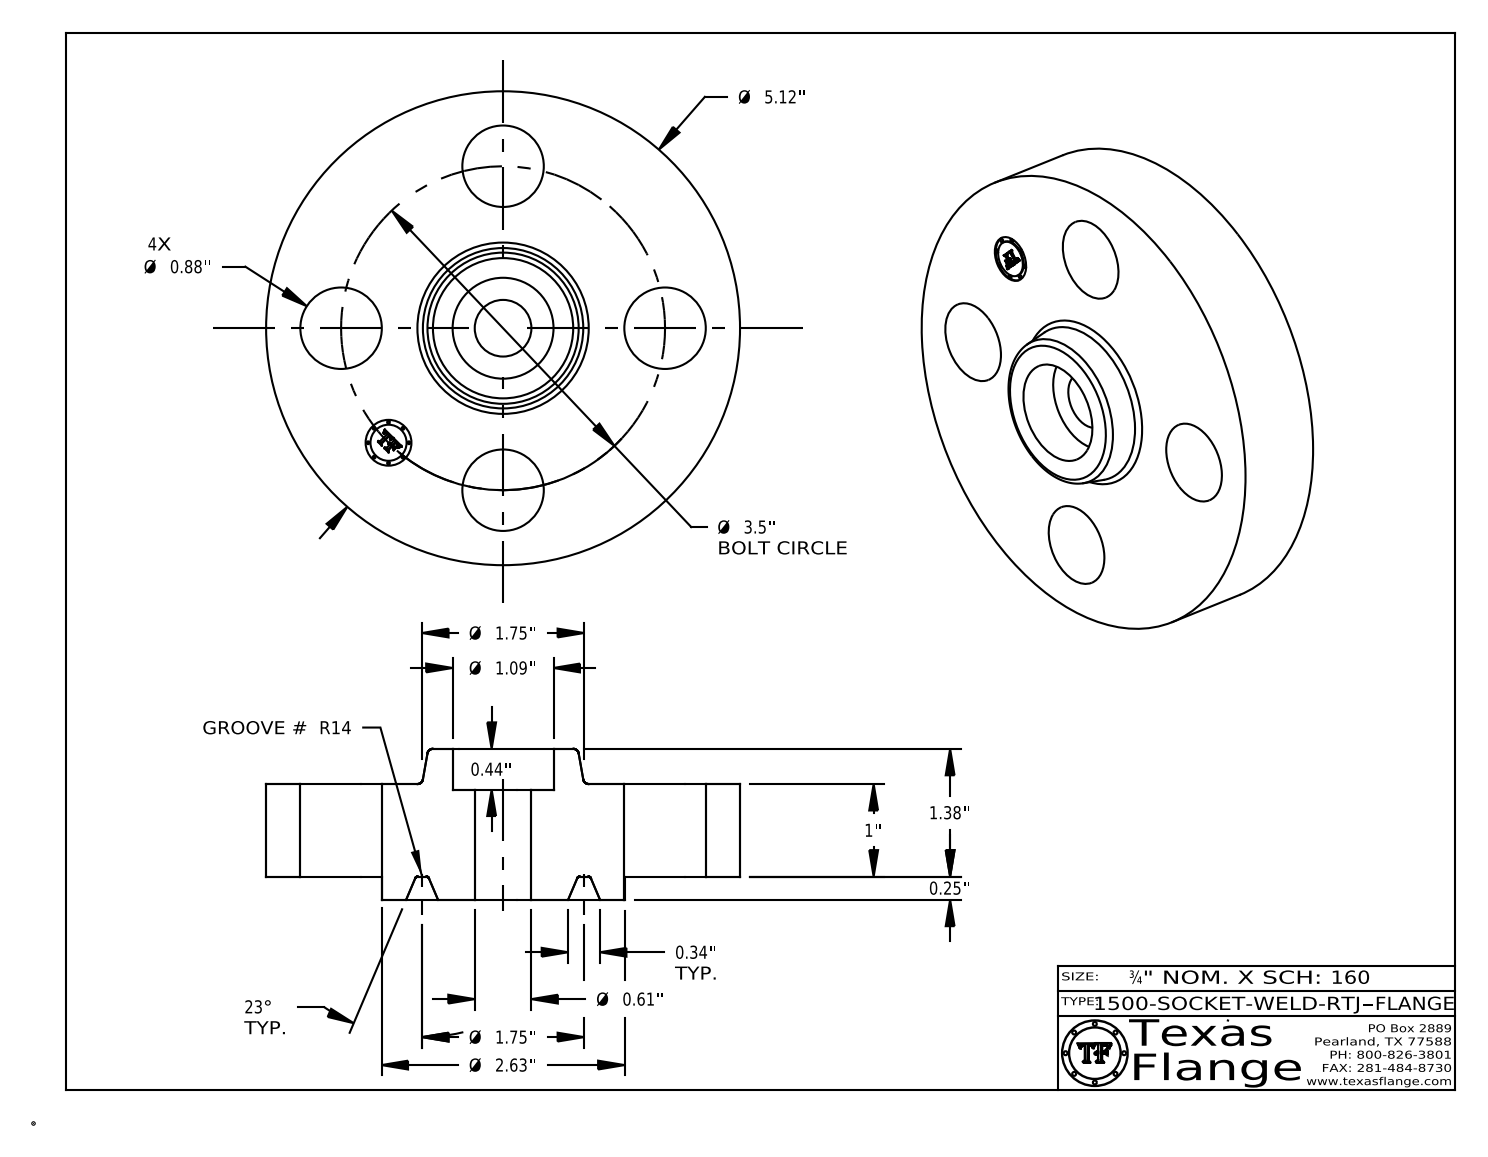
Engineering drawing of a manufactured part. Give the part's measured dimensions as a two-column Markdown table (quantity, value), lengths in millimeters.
| quantity | value |
| --- | --- |
| part name | 1500-SOCKET-WELD-RTJ |
| STEP written by | CATIA V5 STEP AP214 (AUTOMOTIVE_DESIGN) |
| units | millimeters |
| bodies | 1 solid, 426 faces (372 planar, 40 cylindrical, 14 other) |
| overall size | 130 × 130 × 41.4 |
| volume | 315 800 mm³ |
| surface area | 46 510 mm² |
| round holes (diameter × count) | 22.4 × 4, 12.6 × 1, 15.5 × 1, 27.7 × 1 |
| round bosses / shafts (diameter × count) | 0.8 × 8, 130 × 1, 66.7 × 1, 9.9 × 1 |
| main face-to-face distances | 25.4, 6.4, 31.8, 41.4, 35.1, 9.7, 1.5, 30.2, 23.9, 11.2 |
| hole center spacings | 44.5, 62.9, 34, 82.1, 88.9 |
